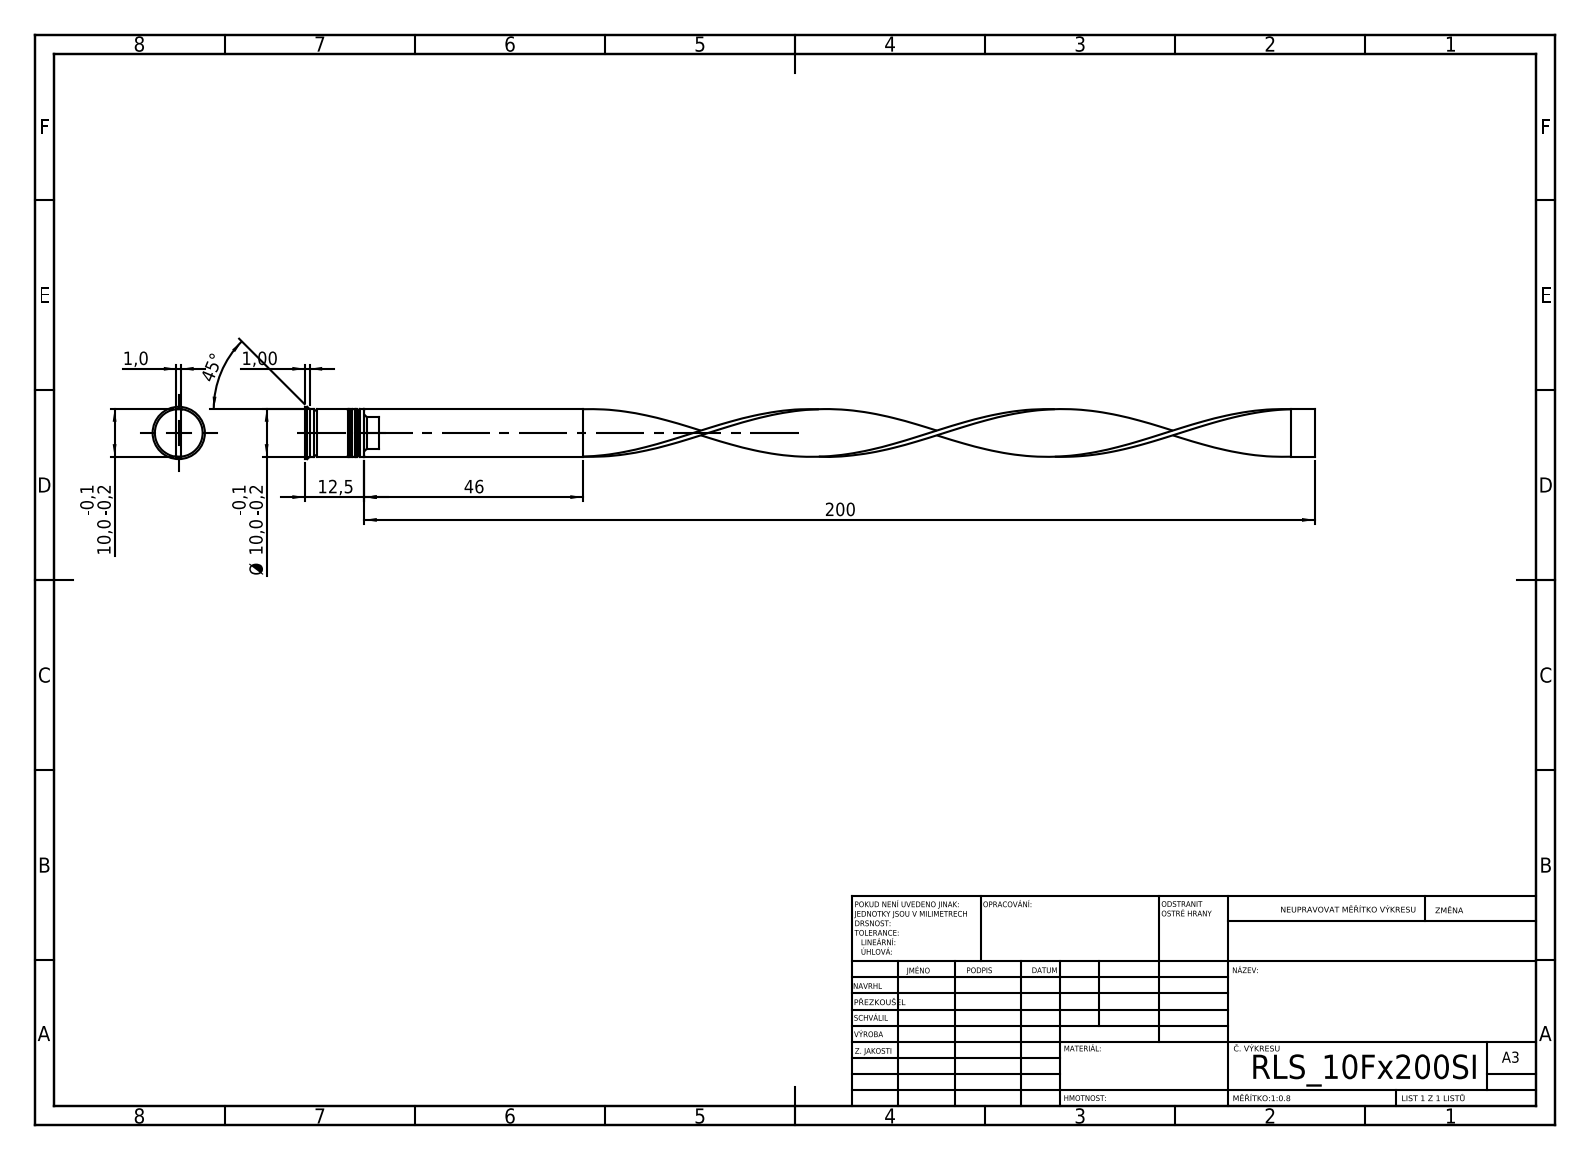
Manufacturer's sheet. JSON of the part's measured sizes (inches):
{"step_written_by": "SolidWorks 2019 (CONFIG_CONTROL_DESIGN)", "units": "inches", "bodies": {"solids": 3, "faces": 96, "planar": 44, "cylindrical": 23, "other": 29}, "overall_size": [8.366, 0.433, 0.433], "volume_in3": 0.191, "surface_area_in2": 8.489, "round_bosses_or_shafts": [[0.433, 1], [0.394, 1], [0.37, 1], [0.276, 1], [0.268, 1]], "face_to_face_distances": [0.039, 0.059, 0.028, 0.087, 0.031, 0.315, 0.394, 0.343, 0.402, 0.374]}
